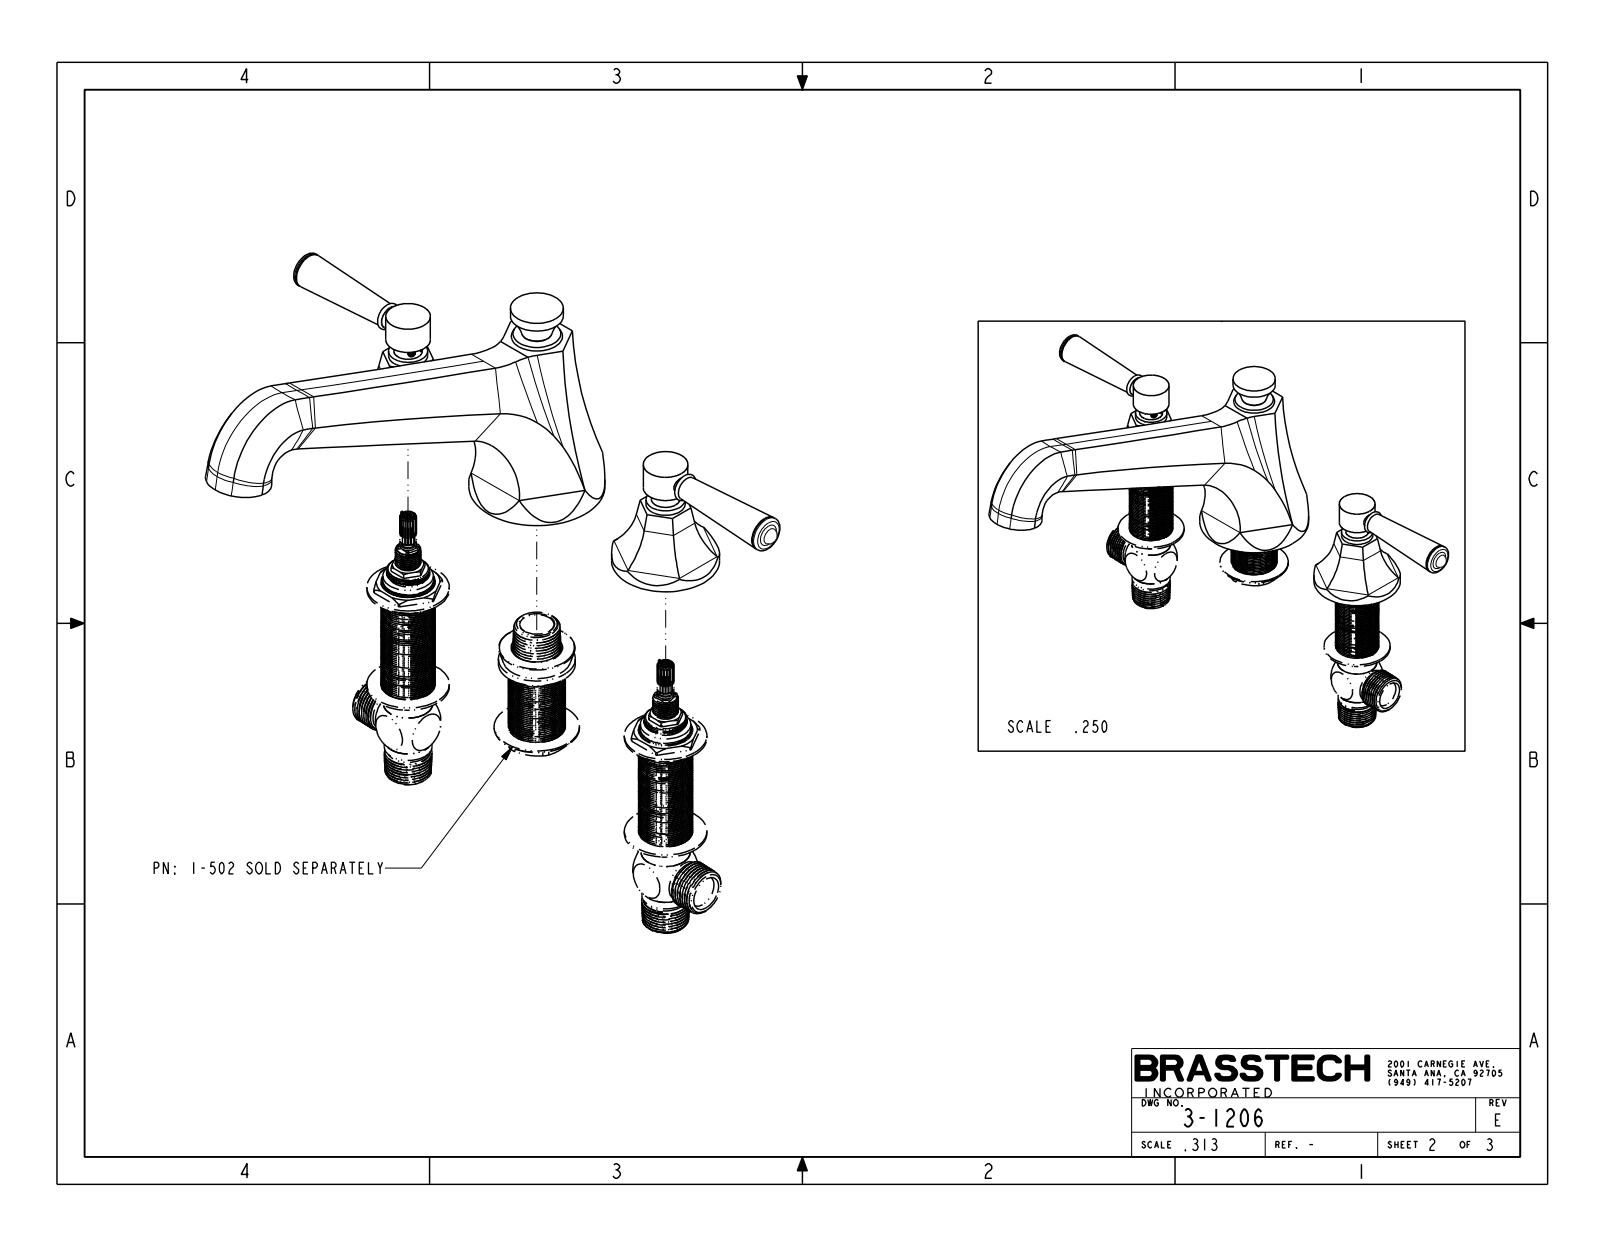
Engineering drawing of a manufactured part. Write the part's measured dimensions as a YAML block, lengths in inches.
part_name: "3-1206"
step_written_by: "CREO PARAMETRIC BY PTC INC, 2018400 (CONFIG_CONTROL_DESIGN)"
units: inches
bodies: {solids: 4, faces: 228, planar: 45, cylindrical: 68, other: 115}
overall_size: [14.786, 11.484, 6.573]
volume: 43.24
surface_area: 137.7
round_holes:
  - {diameter: 0.385, count: 2}
  - {diameter: 0.15, count: 1}
round_bosses_or_shafts:
  - {diameter: 2.375, count: 2}
  - {diameter: 0.98, count: 2}
  - {diameter: 0.86, count: 2}
  - {diameter: 0.792, count: 2}
  - {diameter: 0.625, count: 2}
  - {diameter: 0.365, count: 2}
  - {diameter: 2.99, count: 1}
  - {diameter: 1.16, count: 1}
partial_cylinders:
  - {radius: 1.541, count: 12}
  - {radius: 13, count: 6}
  - {radius: 2.75, count: 1}
face_to_face_distances: [3.928, 4.115, 1.647, 2.468, 2.158, 4.045, 2.398, 0.07, 1.527, 0.12]
